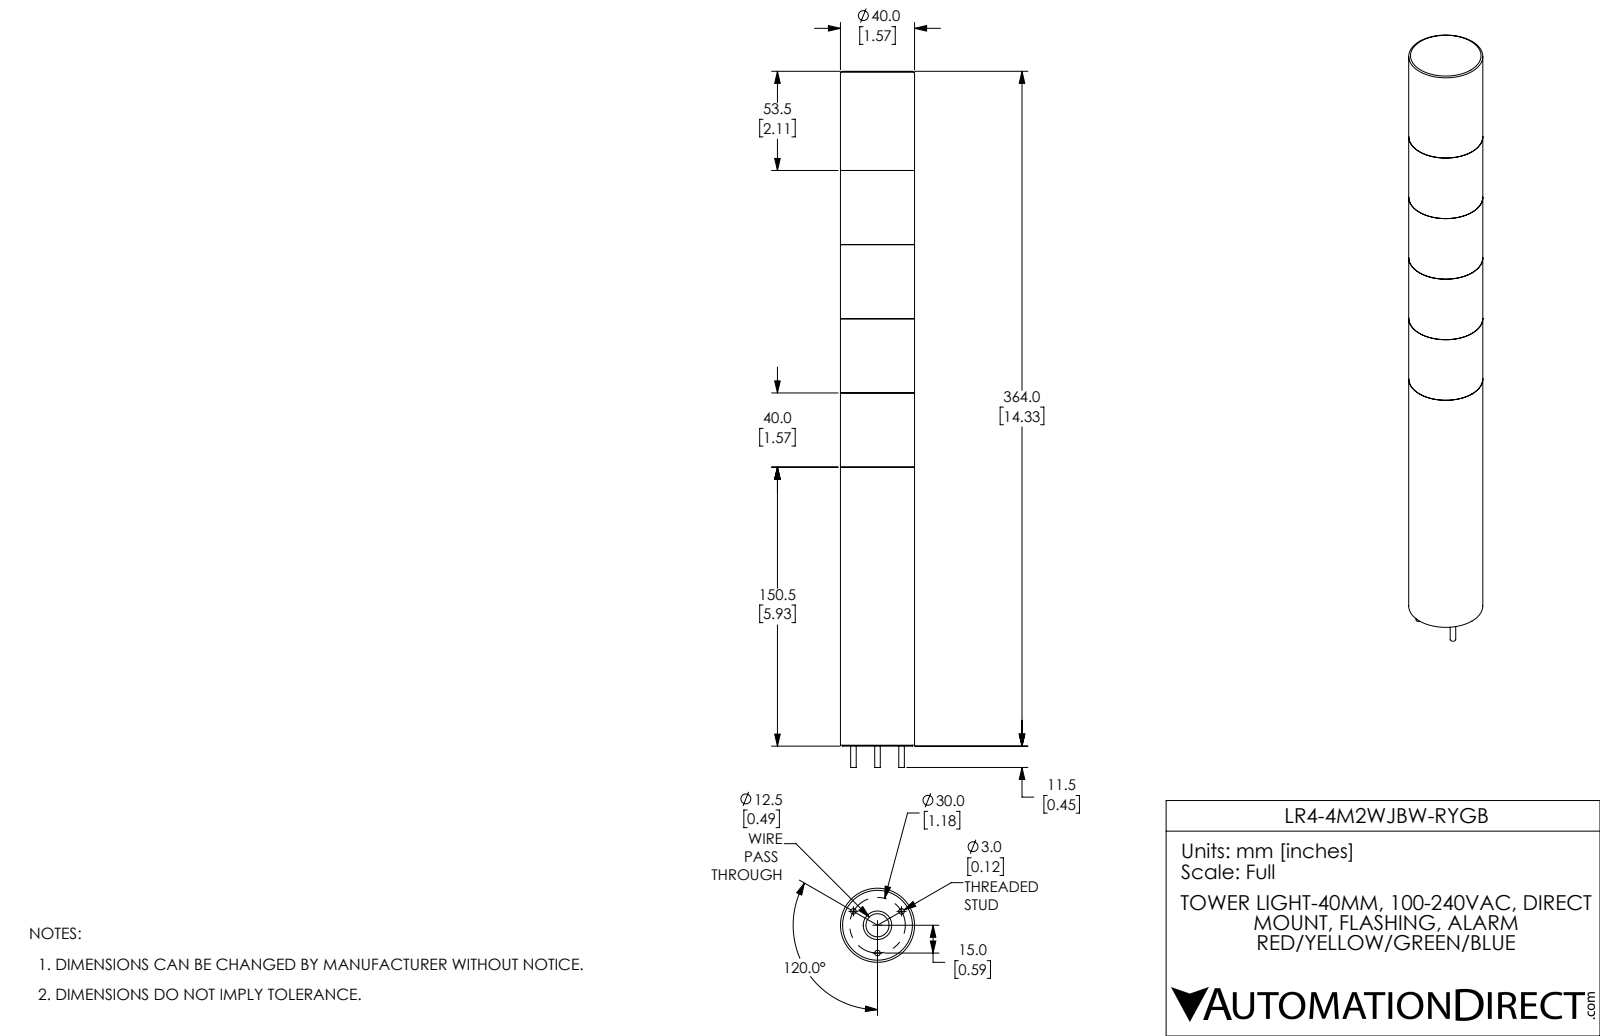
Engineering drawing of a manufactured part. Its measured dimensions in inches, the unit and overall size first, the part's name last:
Units: inches
Overall size (bounding box): 14.783 × 1.575 × 1.575
Round holes (diameter × count): ⌀0.492 ×1, ⌀0.606 ×1, ⌀1.386 ×1, ⌀1.463 ×1, ⌀1.476 ×1
Round bosses / shafts (diameter × count): ⌀0.118 ×3, ⌀1.575 ×1, ⌀1.484 ×1, ⌀1.461 ×1, ⌀1.366 ×1
Main face-to-face distances: 1.575, 3.15, 4.724, 1.701, 0.406, 3.276, 1.98, 4.85, 6.299, 1.169
Volume: 27.79 in³ · Surface area: 113.1 in²
Bodies: 6 solids, 101 faces (37 planar, 62 cylindrical, 2 other)
Part name (STEP PRODUCT): LR4-4M2WJBW-RYGB
STEP written by: SolidWorks 2017 (AUTOMOTIVE_DESIGN)
